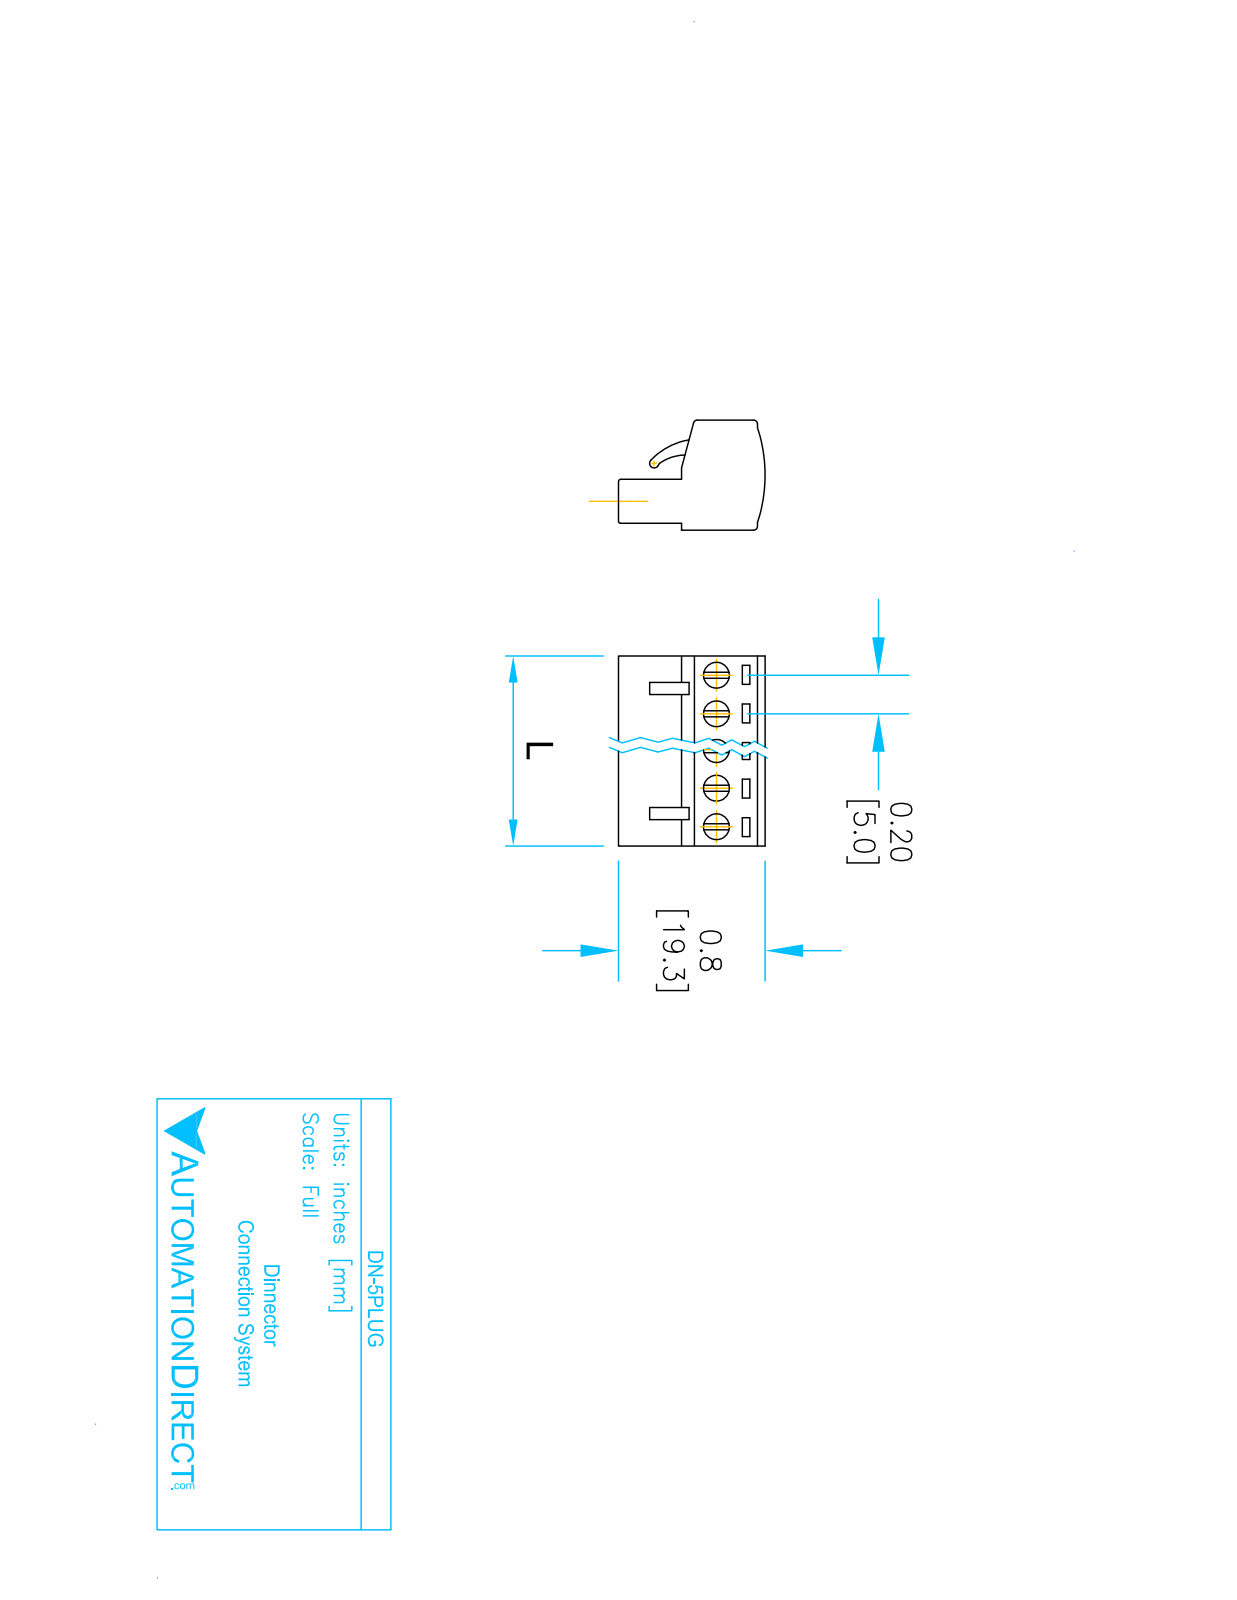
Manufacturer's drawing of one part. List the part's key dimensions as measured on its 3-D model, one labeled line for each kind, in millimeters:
Part name (STEP PRODUCT): 49005_S; 49001_S; 49001_S_49002_SENZA DENTE; 49002_S
STEP written by: SolidWorks 2013 (AUTOMOTIVE_DESIGN)
Units: millimetres
Bodies: 4 solids, 449 faces (313 planar, 111 cylindrical, 25 other)
Overall size (bounding box): 25.4 × 19.3 × 14.5
Volume: 4 352 mm³ · Surface area: 4 344 mm²
Round holes (diameter × count): ⌀1.6 ×5, ⌀2.5 ×5, ⌀3.4 ×5, ⌀3.6 ×5
Round bosses / shafts (diameter × count): ⌀3 ×5
Partial cylindrical surfaces — rounded edges, fillets, slot ends (radius × count): R2.9 ×5, R0.5 ×3, R0.3 ×2, R0.6 ×1, R6 ×1, R9 ×1, R20.03 ×1
Main face-to-face distances: 5.08, 10.16, 15.24, 20.32, 6.7, 1, 25.4, 14.5, 7.8, 0.79
Hole centre spacings: 5.08, 10.16, 15.24, 20.32
